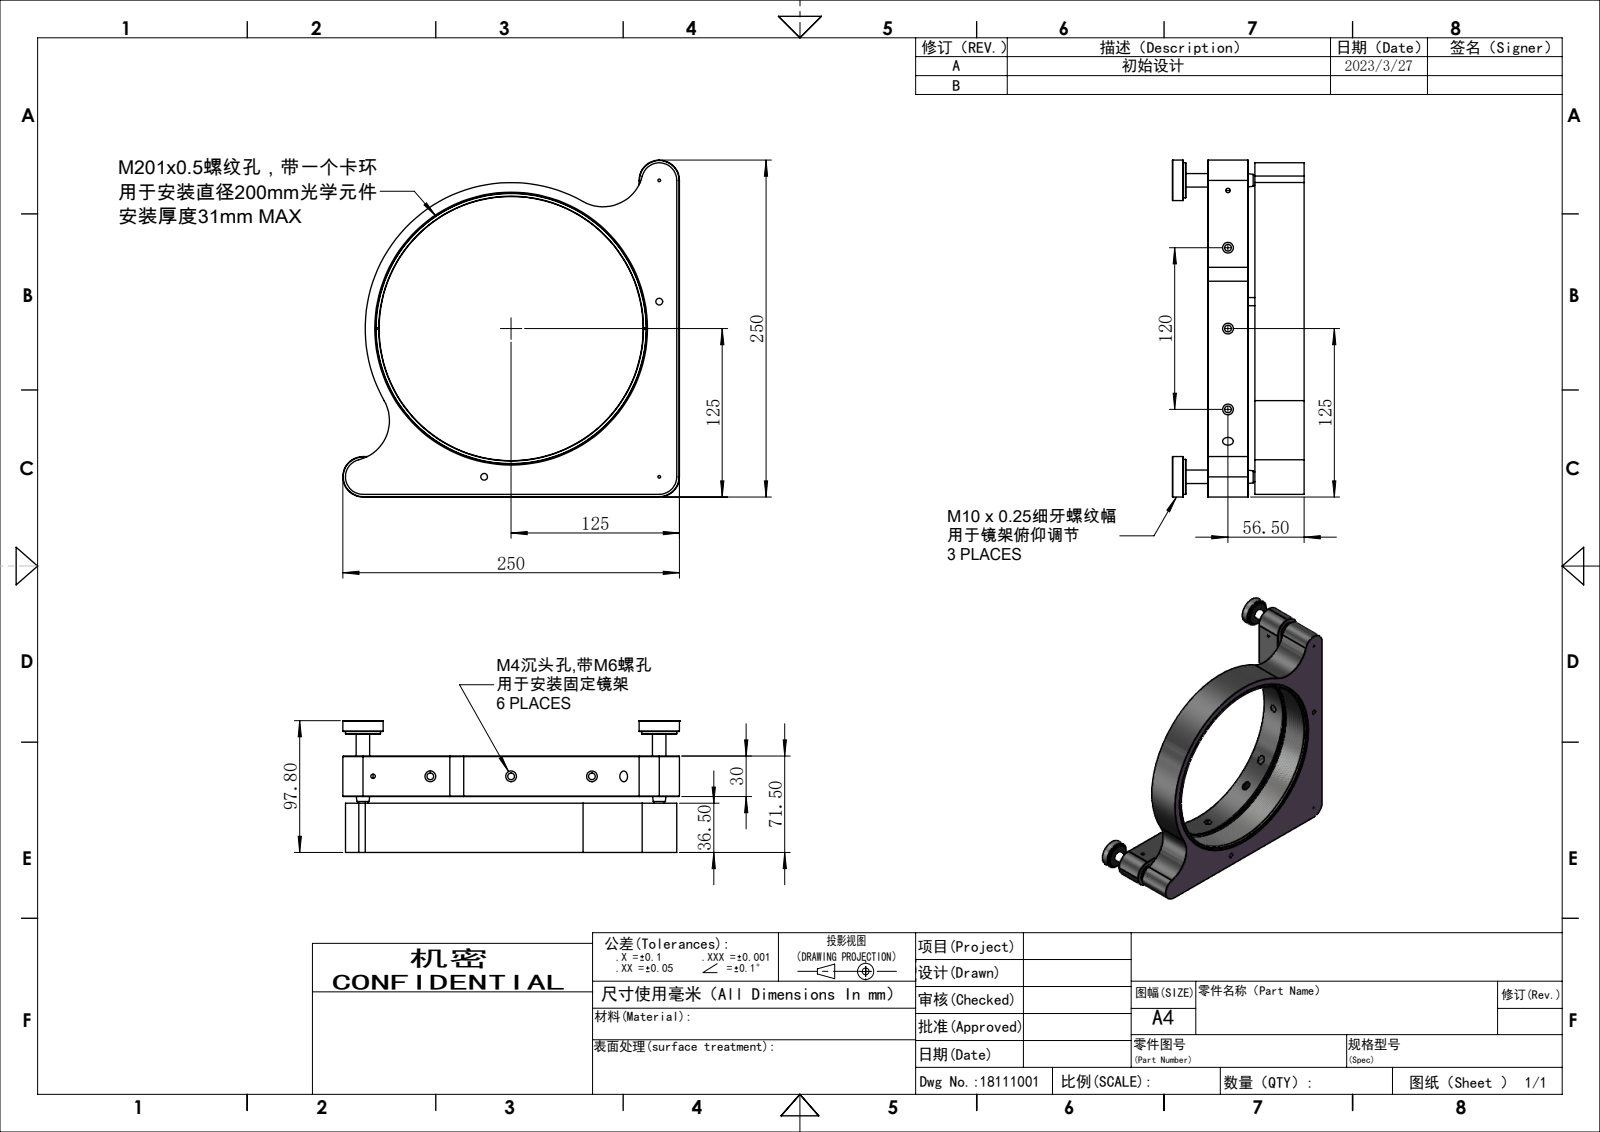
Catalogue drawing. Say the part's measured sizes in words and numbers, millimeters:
Its 3-D file was written by "SolidWorks 2021 (CONFIG_CONTROL_DESIGN)". It is 0 solids with 358 faces: 117 planar, 166 cylindrical and 75 other. Overall it measures 250 by 250 by 97.75 millimeters. Round holes: 8 of diameter 3.3, 8 of diameter 5, 6 of diameter 8, 6 of diameter 9, 3 of diameter 7, 3 of diameter 15, 2 of diameter 2, 2 of diameter 13, 1 of diameter 20.5, 1 of diameter 196, 1 of diameter 196.7, 1 of diameter 200.5. Round bosses or shafts: 3 of diameter 30, 3 of diameter 26, 3 of diameter 10, 2 of diameter 20, 1 of diameter 201, 1 of diameter 10.2, 1 of diameter 2. Partial cylindrical surfaces (rounded edges, fillets, slot ends): 12 of radius 1.05, 4 of radius 2, 4 of radius 6, 4 of radius 30, 2 of radius 40, 1 of radius 10, 1 of radius 103, 1 of radius 108.35. The main face-to-face distances are 30, 36.5, 5, 41.5, 35, 71.5, 2, 28, 10, 0.5. The hole center spacings are 60, 130, 95, 35, 42.5, 102.5, 155.56, 162.5.
